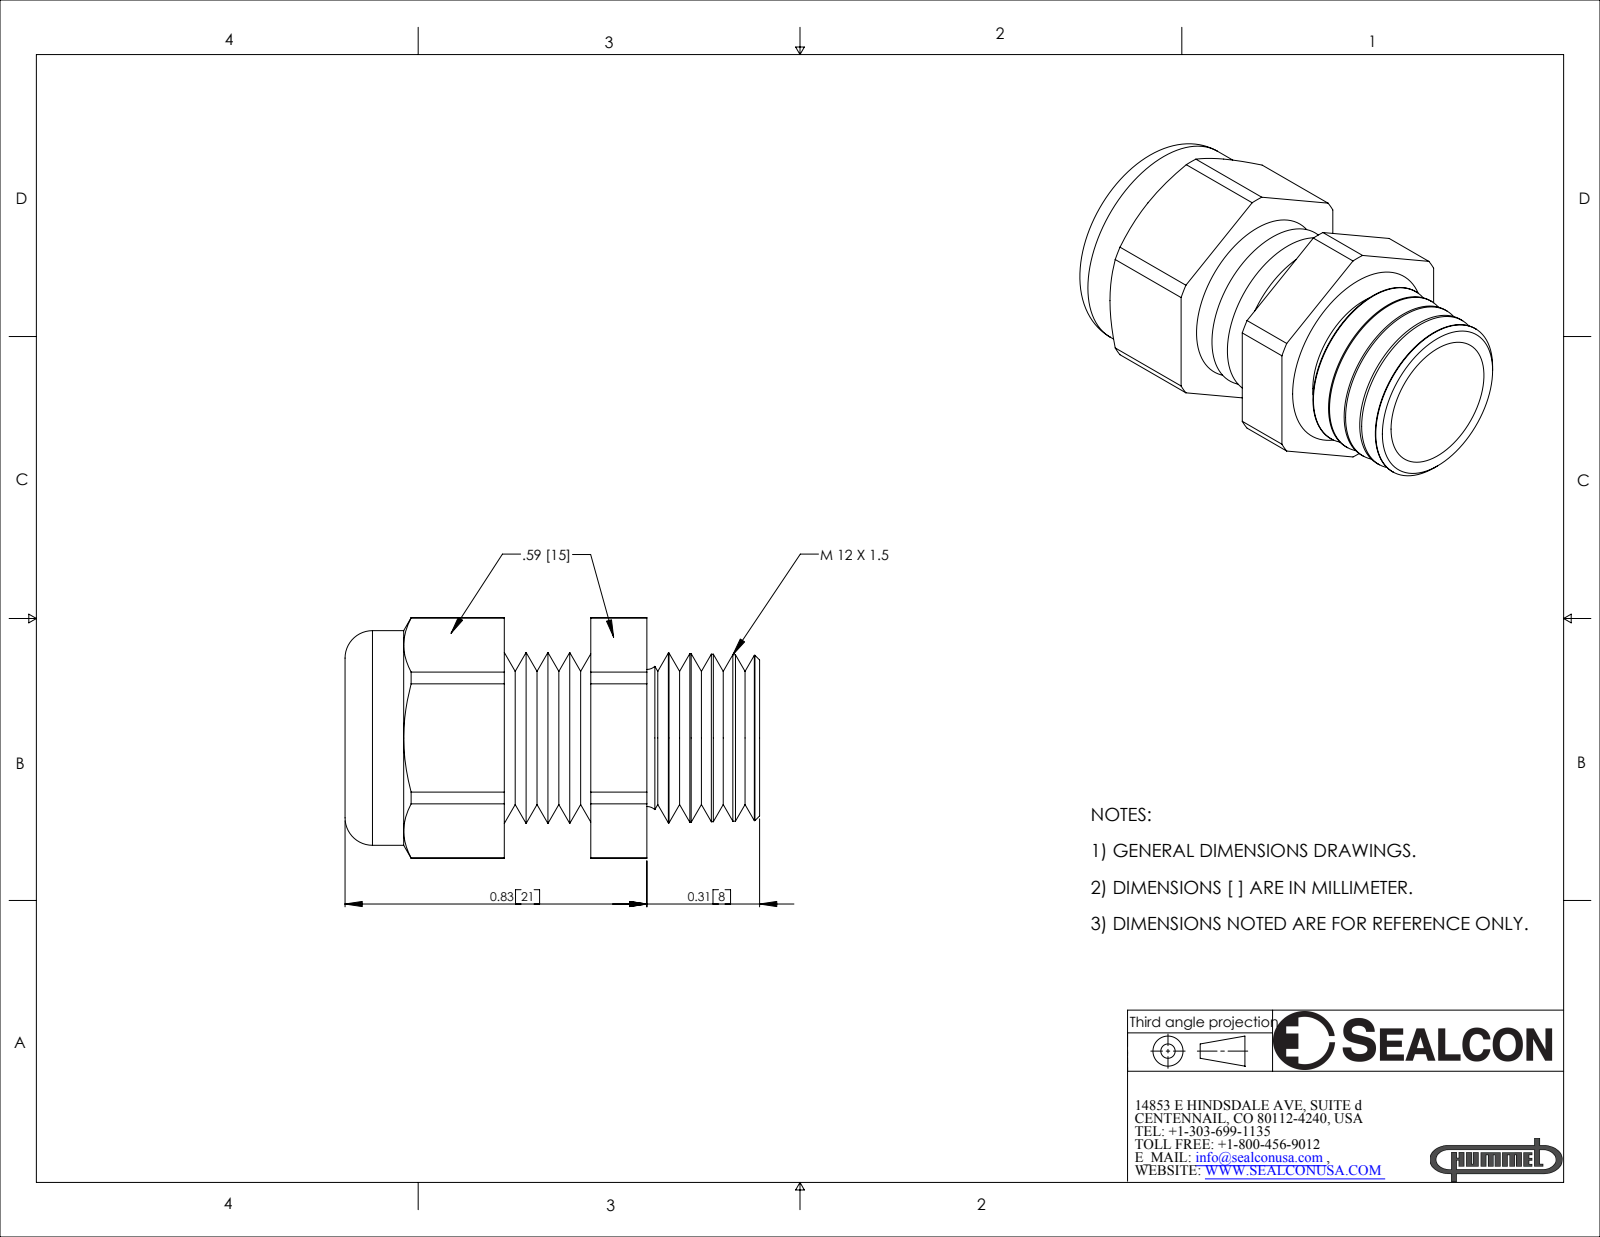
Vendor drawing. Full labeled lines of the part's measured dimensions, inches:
Part name (STEP PRODUCT): CD12MA
STEP written by: SolidWorks 2007 (CONFIG_CONTROL_DESIGN)
Units: inches
Bodies: 2 solids, 108 faces (20 planar, 24 cylindrical, 64 other)
Overall size (bounding box): 1.14 × 0.661 × 0.59
Volume: 0.151 in³ · Surface area: 4.819 in²
Round holes (diameter × count): ⌀0.3 ×1, ⌀0.4 ×1, ⌀0.47 ×1
Round bosses / shafts (diameter × count): ⌀0.59 ×1
Partial cylindrical surfaces — rounded edges, fillets, slot ends (radius × count): R0.33 ×1
Main face-to-face distances: 0.59, 0.238, 0.277, 0.515, 0.669, 0.392, 0.154, 0.131, 0.408, 0.646
